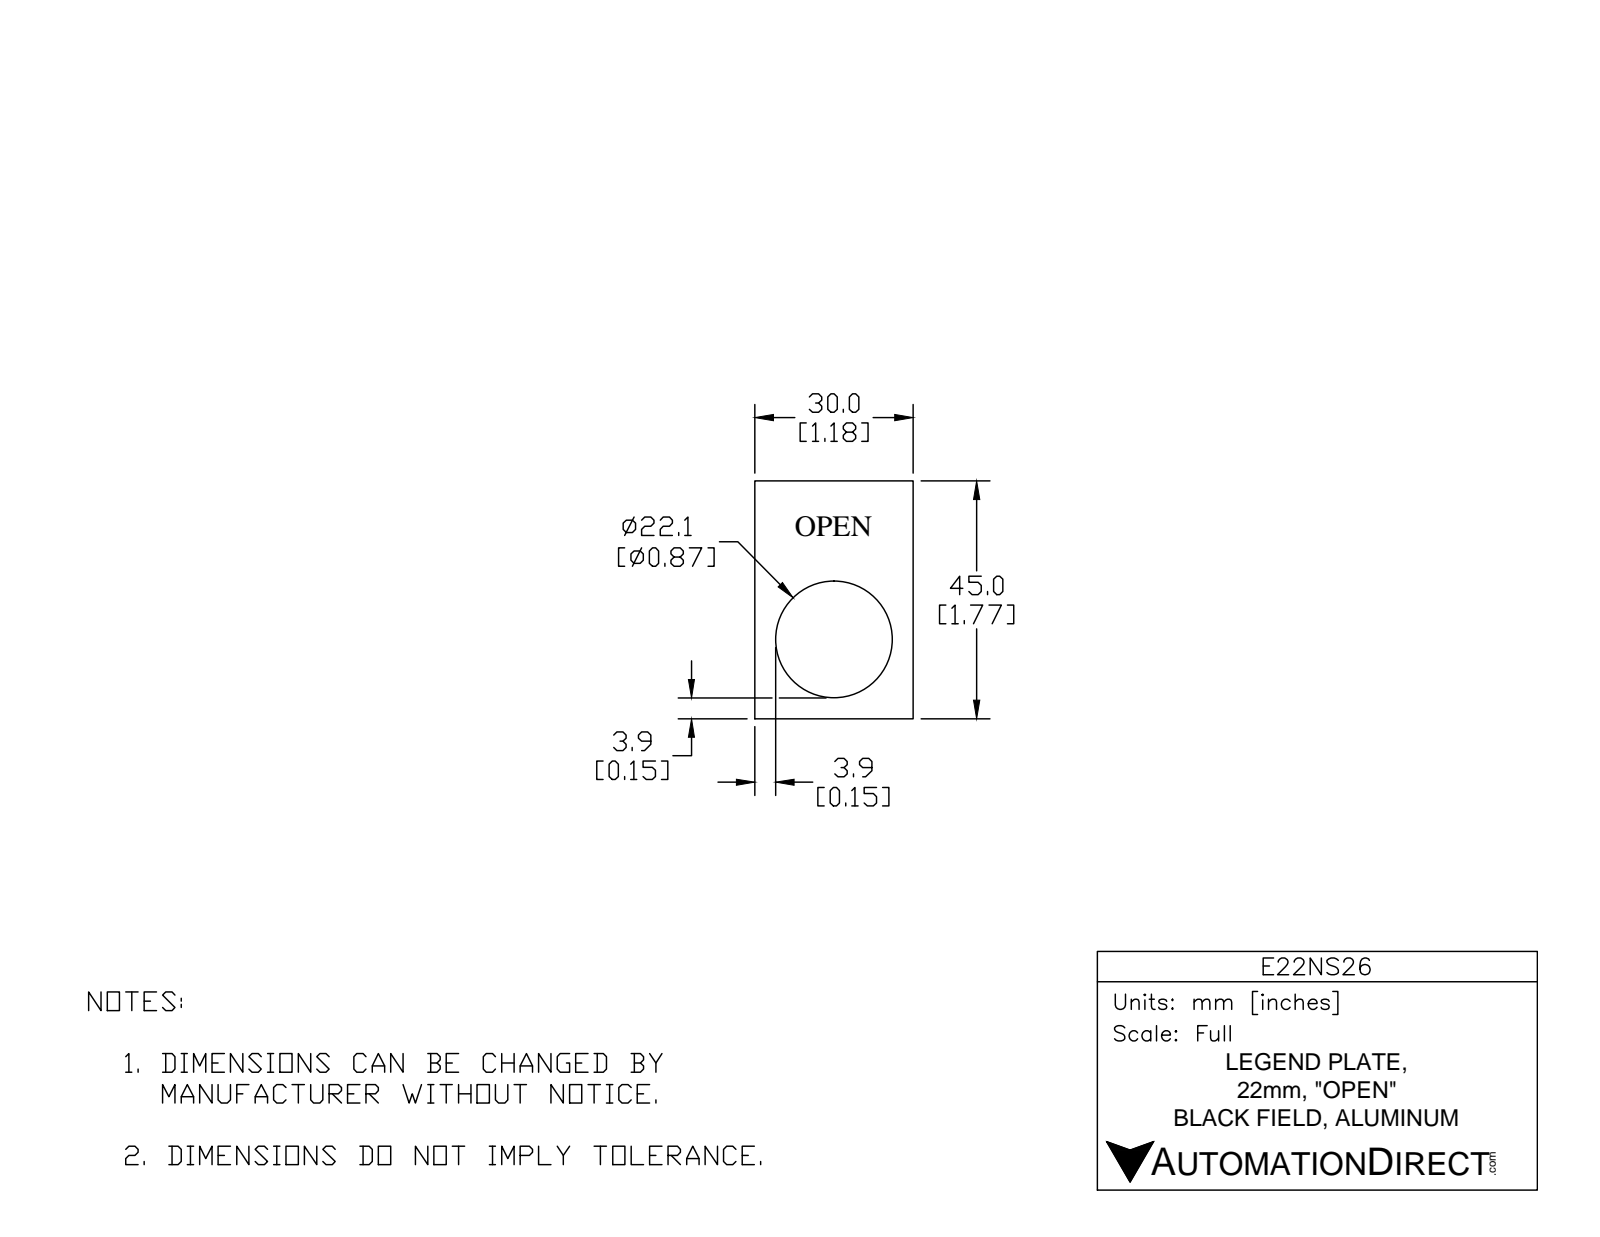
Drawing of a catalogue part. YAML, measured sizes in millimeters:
part_name: "E22NS26"
step_written_by: "SolidWorks 2017 (AUTOMOTIVE_DESIGN)"
units: millimeters
bodies: {solids: 1, faces: 62, planar: 45, cylindrical: 3, other: 14}
overall_size: [45, 30, 1.3]
volume: 1251
surface_area: 2239
round_holes:
  - {diameter: 22.2, count: 1}
face_to_face_distances: [1.3, 30, 45, 1.05, 4.7, 40.3, 0.36, 6.26, 13.4, 16.6]
